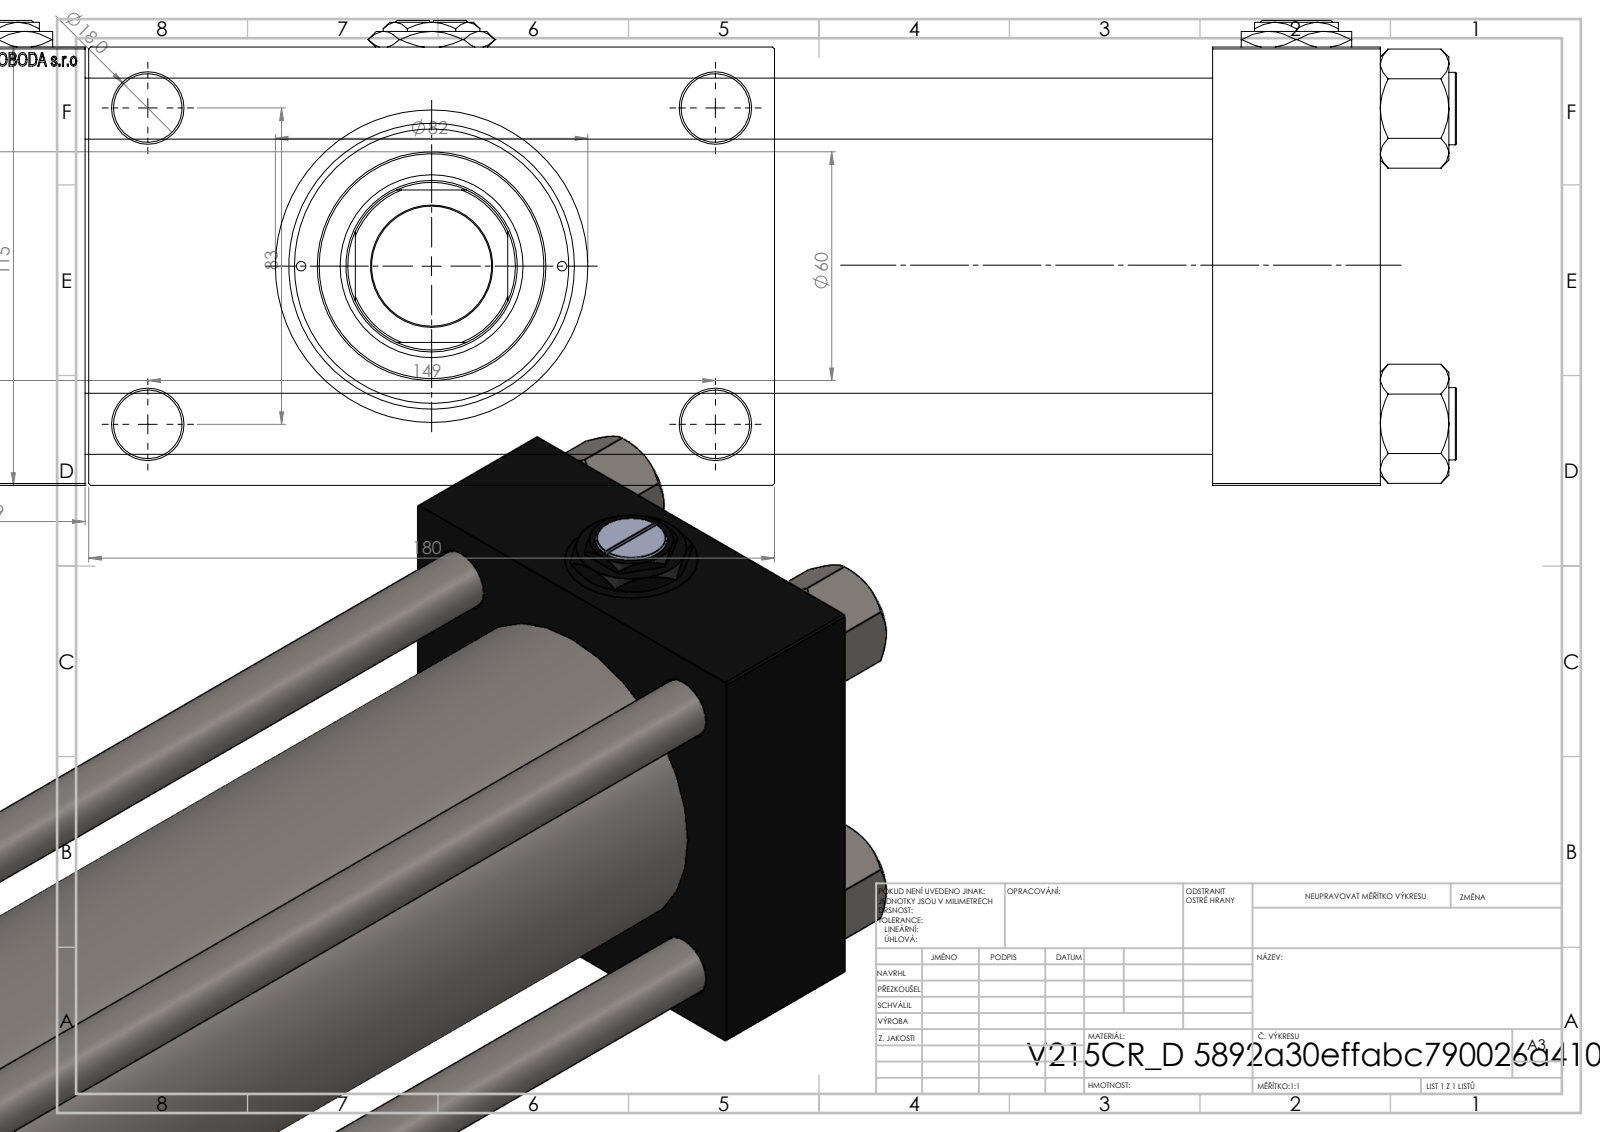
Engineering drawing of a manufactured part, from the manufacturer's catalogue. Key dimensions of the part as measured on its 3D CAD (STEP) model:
Part name (STEP PRODUCT): V215CR_VCP_D; NUT_M5_D; V215CR_D_TYCINKA; V215CR_D_Body (+2 more)
STEP written by: SolidWorks 2019 (CONFIG_CONTROL_DESIGN)
Units: millimetres
Bodies: 13 solids, 1260 faces (595 planar, 103 cylindrical, 562 other)
Overall size (bounding box): 460 × 180 × 122
Volume: 2 721 000 mm³ · Surface area: 507 748 mm²
Round holes (diameter × count): ⌀16 ×4, ⌀18 ×4, ⌀26.44 ×4, ⌀35 ×4, ⌀7 ×3, ⌀2.5 ×2, ⌀31.5 ×1, ⌀45 ×1, ⌀48 ×1, ⌀61 ×1, ⌀72 ×1, ⌀80 ×1
Round bosses / shafts (diameter × count): ⌀19 ×4, ⌀86 ×1, ⌀82 ×1, ⌀60 ×1
Partial cylindrical surfaces — rounded edges, fillets, slot ends (radius × count): R22 ×1
Main face-to-face distances: 115, 296, 345, 49, 44, 340, 389, 32.5, 147.5, 180
Hole centre spacings: 33.15, 41.96, 57.81, 58.48, 82.7, 85.28, 86.17, 89.24
